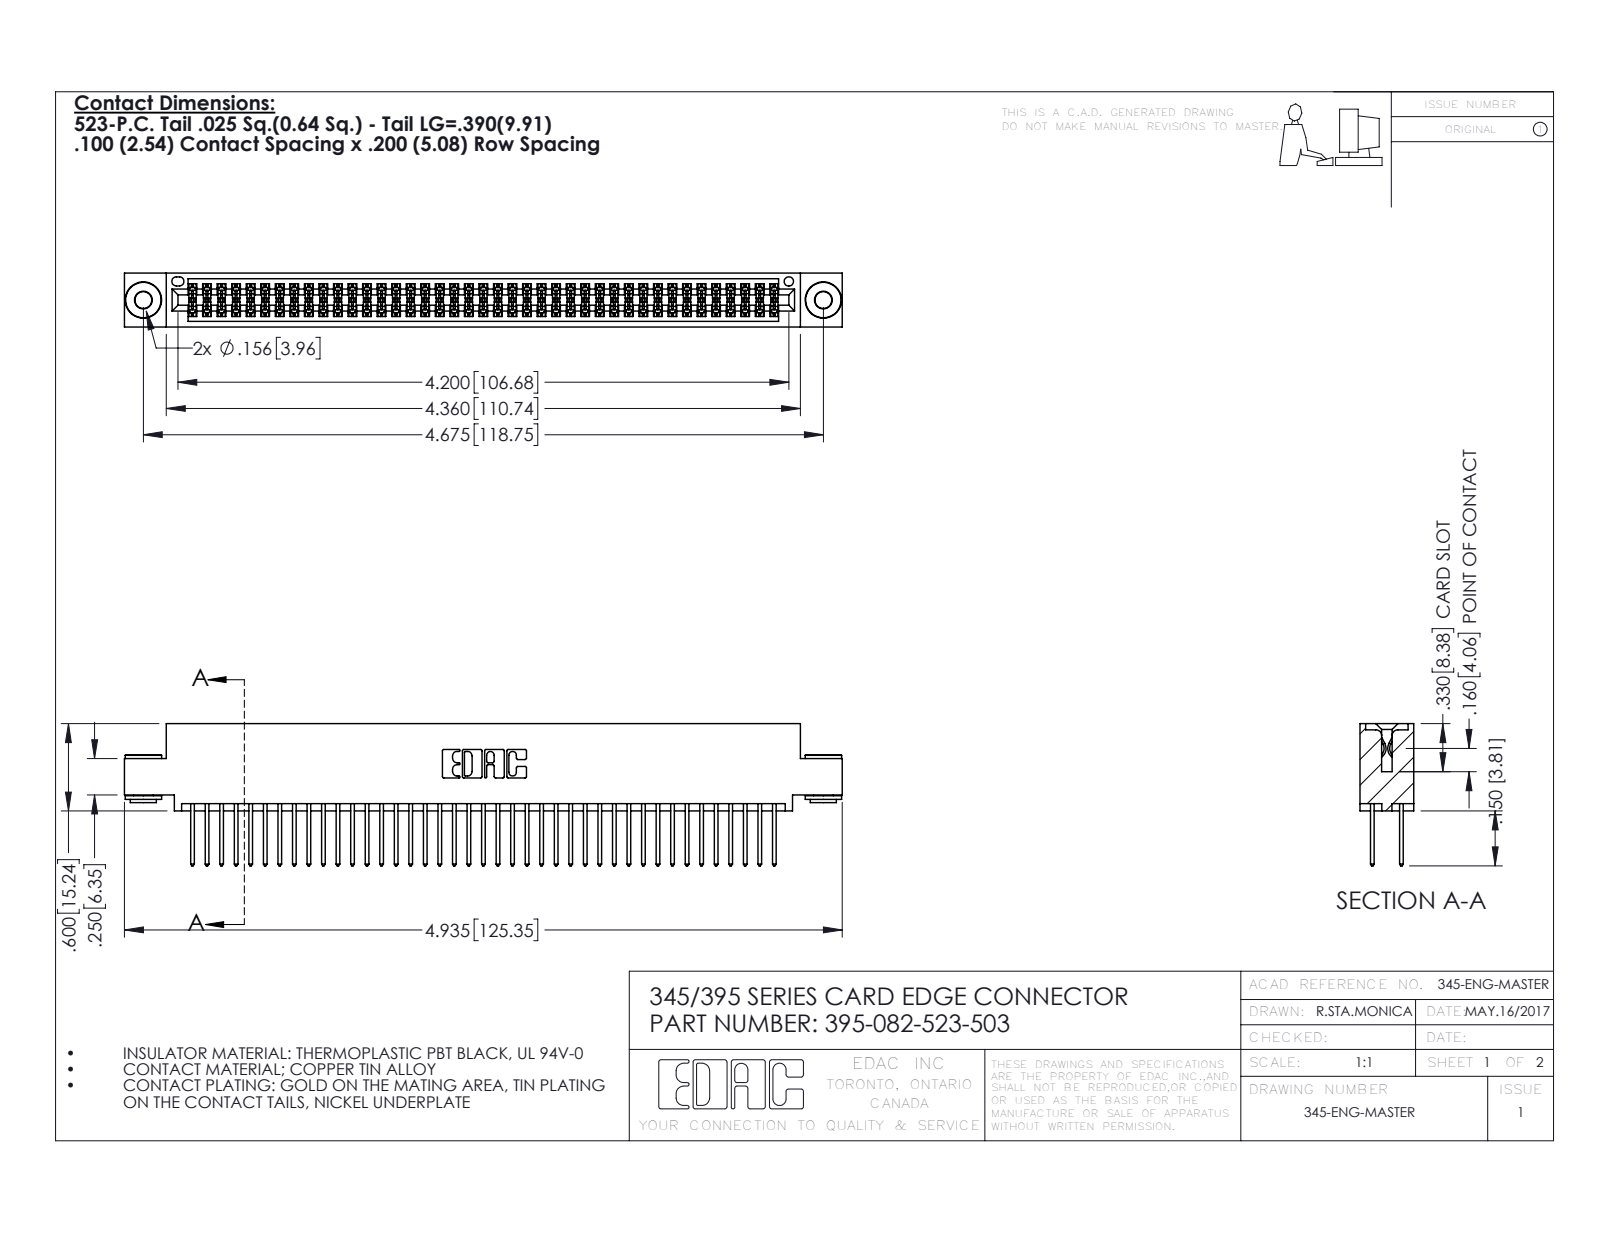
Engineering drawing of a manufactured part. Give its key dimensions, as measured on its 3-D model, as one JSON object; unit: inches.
{"part_name": "345-250-002_345-250-002-102; 345 Part_0.110 Offset - 0.156 Dia-TH; 345-292-001_345-293-123; 395-082-523-503", "step_written_by": "SolidWorks 2016 (CONFIG_CONTROL_DESIGN)", "units": "inches", "bodies": {"solids": 85, "faces": 4268, "planar": 2800, "cylindrical": 1460, "other": 8}, "overall_size": [4.935, 0.977, 0.37], "volume_in3": 0.749, "surface_area_in2": 29.74, "round_holes": [[0.116, 2], [0.156, 2], [0.064, 1]], "round_bosses_or_shafts": [[0.25, 2], [0.18, 2], [0.136, 2]], "partial_cylinders_radius": [[0.006, 123], [0.01, 82], [0.01, 22], [0.007, 6], [0.031, 6], [0.026, 3], [0.014, 2], [0.019, 2]], "face_to_face_distances": [0.072, 0.298, 0.2, 0.025, 0.098, 0.272, 0.37, 0.225, 0.175, 0.149], "hole_center_spacings": [0.27, 4.439, 4.675]}
